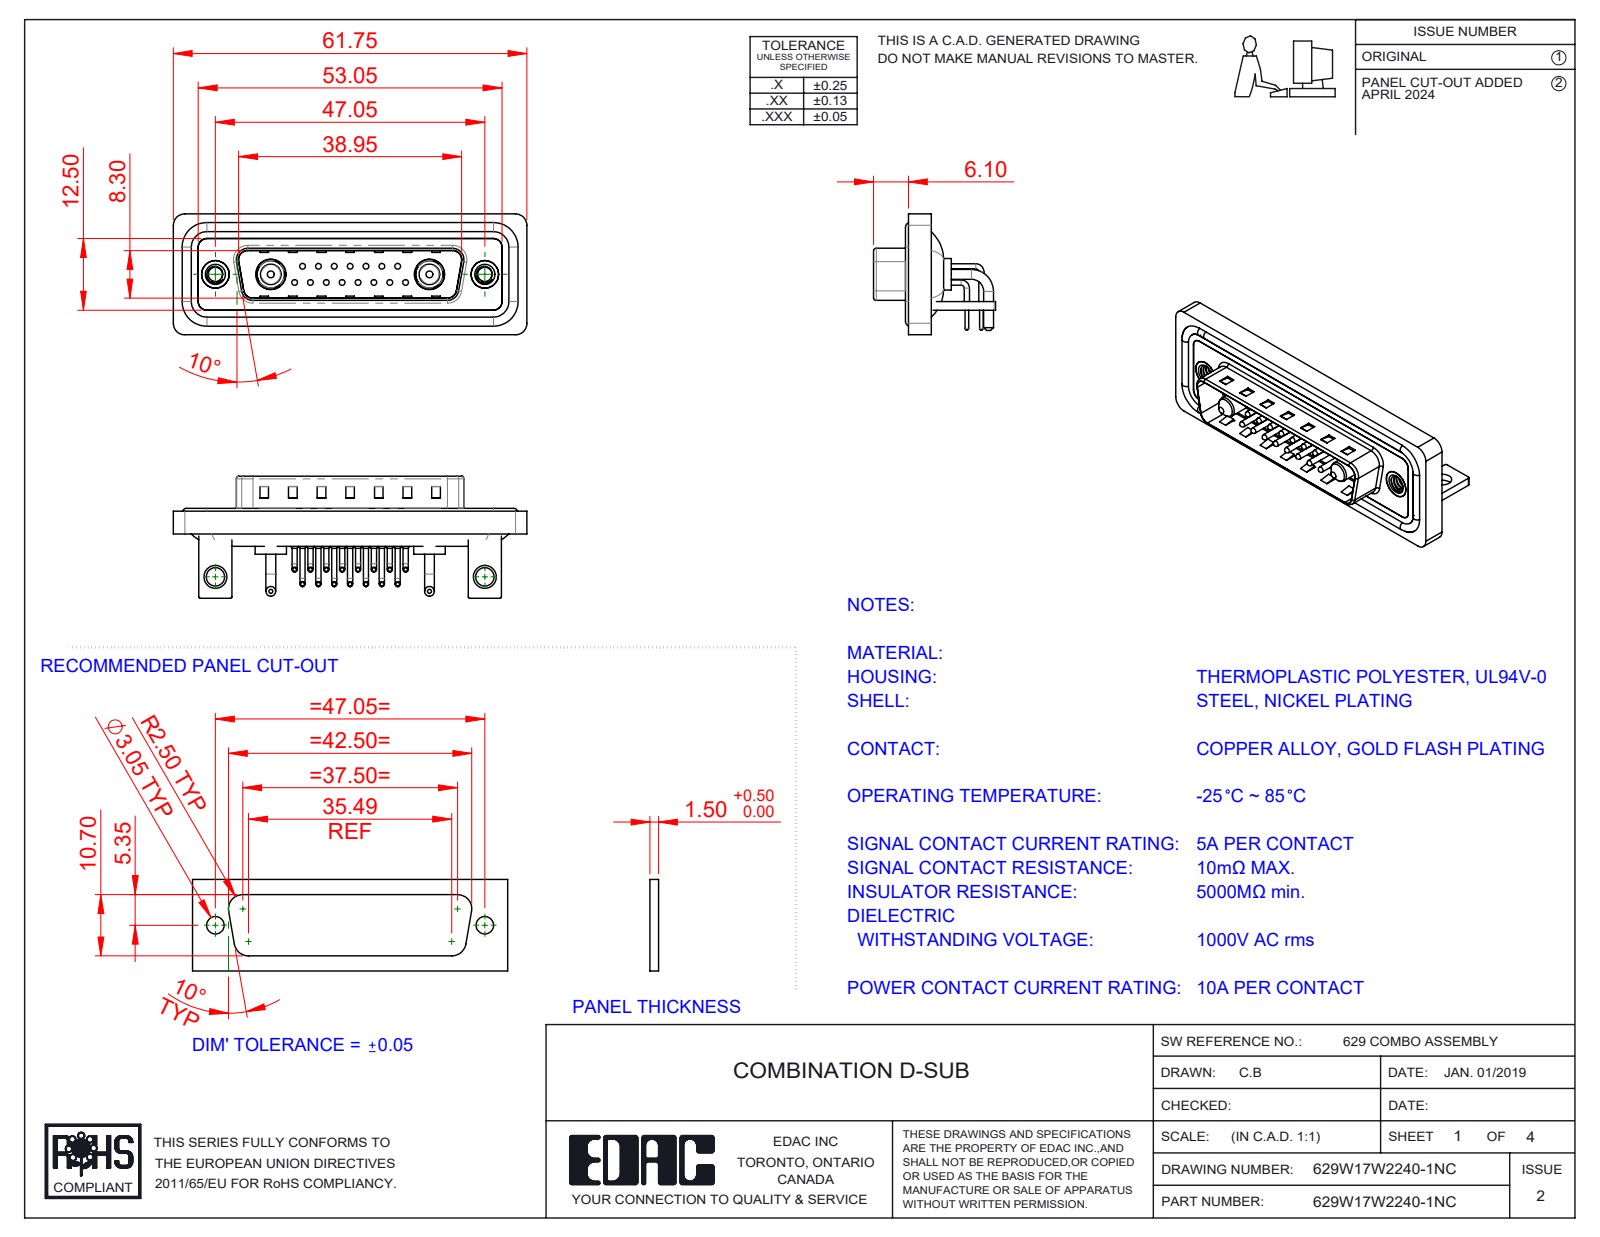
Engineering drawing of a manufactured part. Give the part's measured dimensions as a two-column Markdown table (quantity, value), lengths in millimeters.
| quantity | value |
| --- | --- |
| part name | 629Combo Waterproof Housing_25 Contacts; 629Combo Shell Front_25 Contacts; 629Combo Contact Row 1; 629Combo Stabilizer Bracket (+6 more) |
| STEP written by | SolidWorks 2023 (CONFIG_CONTROL_DESIGN) |
| units | millimeters |
| bodies | 28 solids, 2257 faces (1209 planar, 788 cylindrical, 260 other) |
| overall size | 61.75 × 21.3 × 21.1 |
| volume | 7 668 mm³ |
| surface area | 13 087 mm² |
| round holes (diameter × count) | 0.75 × 15, 1.6 × 15, 2 × 15, 2.5 × 2, 3.2 × 2, 4 × 2, 4.8 × 2, 4.85 × 2, 5 × 2, 5.3 × 2 |
| round bosses / shafts (diameter × count) | 0.9 × 30, 1.5 × 15, 1 × 15, 0.65 × 15, 1.7 × 4, 1.6 × 4, 5.5 × 2, 5.2 × 2 |
| partial cylindrical surfaces (radius × count) | 2 × 19, 1.5 × 18, 0.25 × 16, 1.01 × 15, 0.5 × 9, 1.6 × 8, 0.6 × 4, 0.65 × 4 |
| main face-to-face distances | 0.4, 0.8, 1.5, 2.1, 2.9, 1.1, 4.1, 1.6, 4.5, 3.7 |
| hole center spacings | 3.16, 2.77, 5.54, 8.31, 5.04, 7.49, 11.08, 5.03 |
